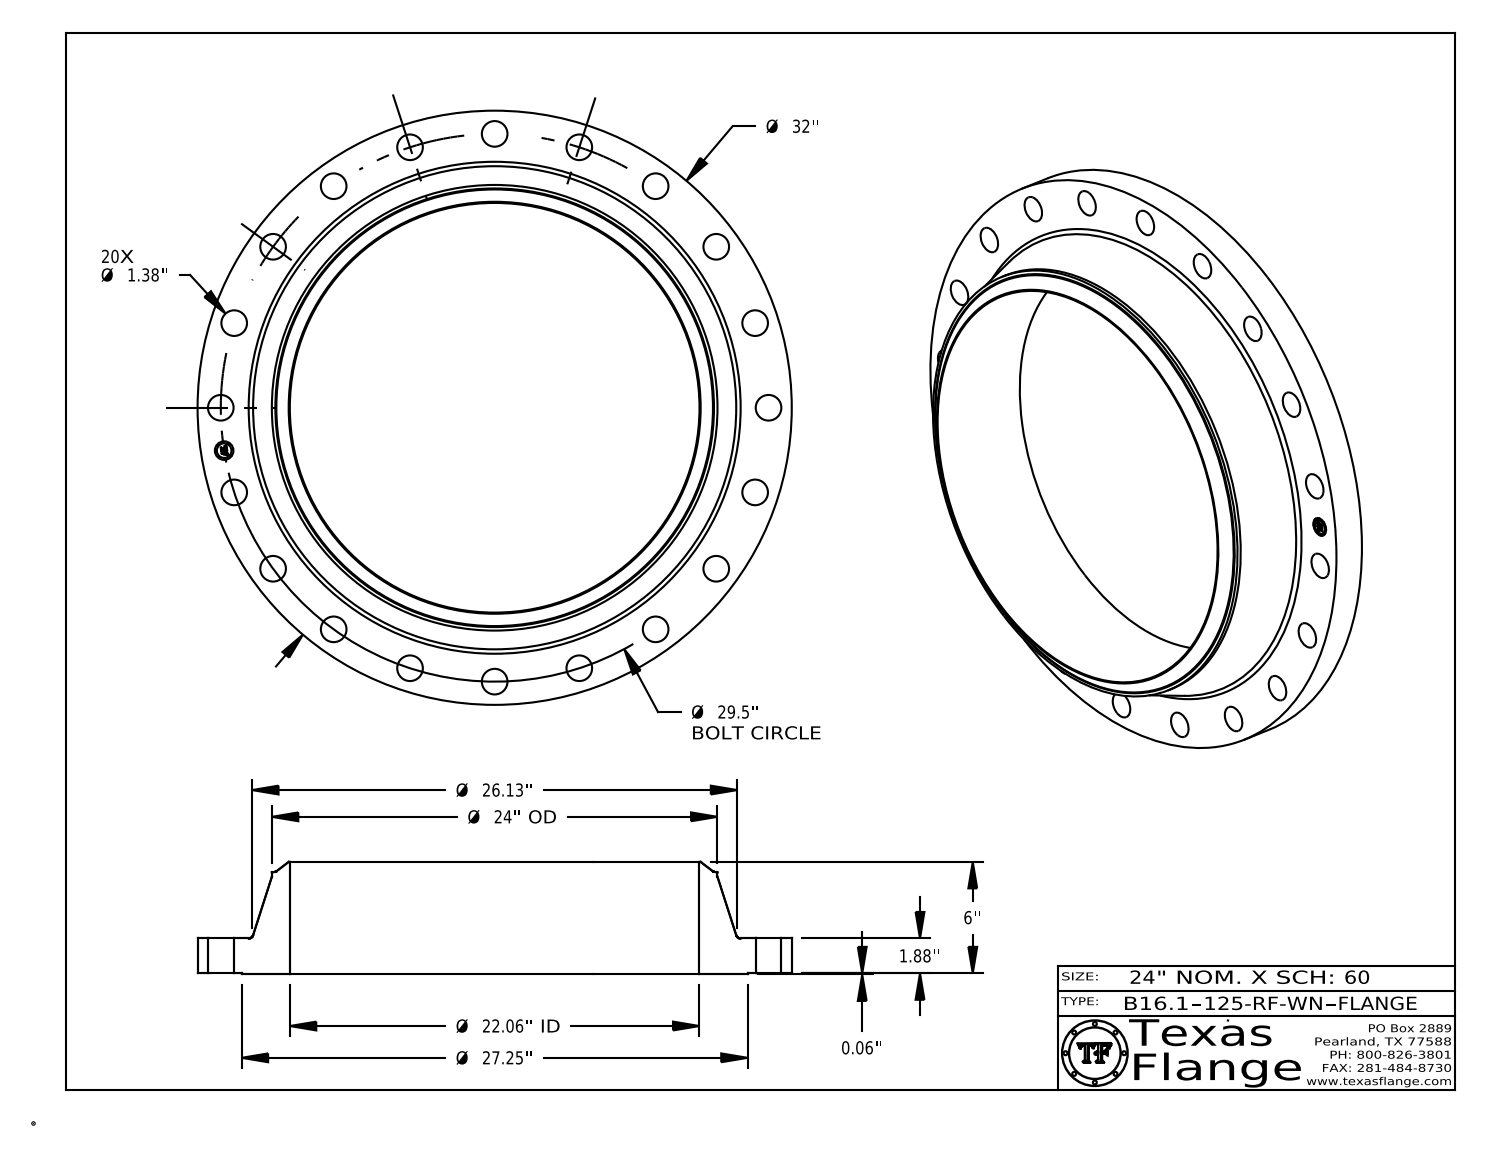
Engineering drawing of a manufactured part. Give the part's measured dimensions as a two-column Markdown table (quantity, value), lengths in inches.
| quantity | value |
| --- | --- |
| part name | B16.1, Class 125-RF-WN |
| STEP written by | CATIA V5 STEP AP214 (AUTOMOTIVE_DESIGN) |
| units | inches |
| bodies | 1 solid, 447 faces (369 planar, 68 cylindrical, 10 other) |
| overall size | 32 × 32 × 6.063 |
| volume | 1 154 in³ |
| surface area | 1 779 in² |
| round holes (diameter × count) | 1.38 × 20, 1 × 1, 22.062 × 1 |
| round bosses / shafts (diameter × count) | 0.061 × 8, 32 × 1, 27.25 × 1, 24 × 1, 0.788 × 1 |
| main face-to-face distances | 1.943, 0.063, 1.88, 6.063, 6, 4.12, 1.928, 1.865, 0.015, 4.135 |
| hole center spacings | 14.75, 29.137, 4.615, 17.34, 20.859, 23.866, 26.285, 9.116 |
